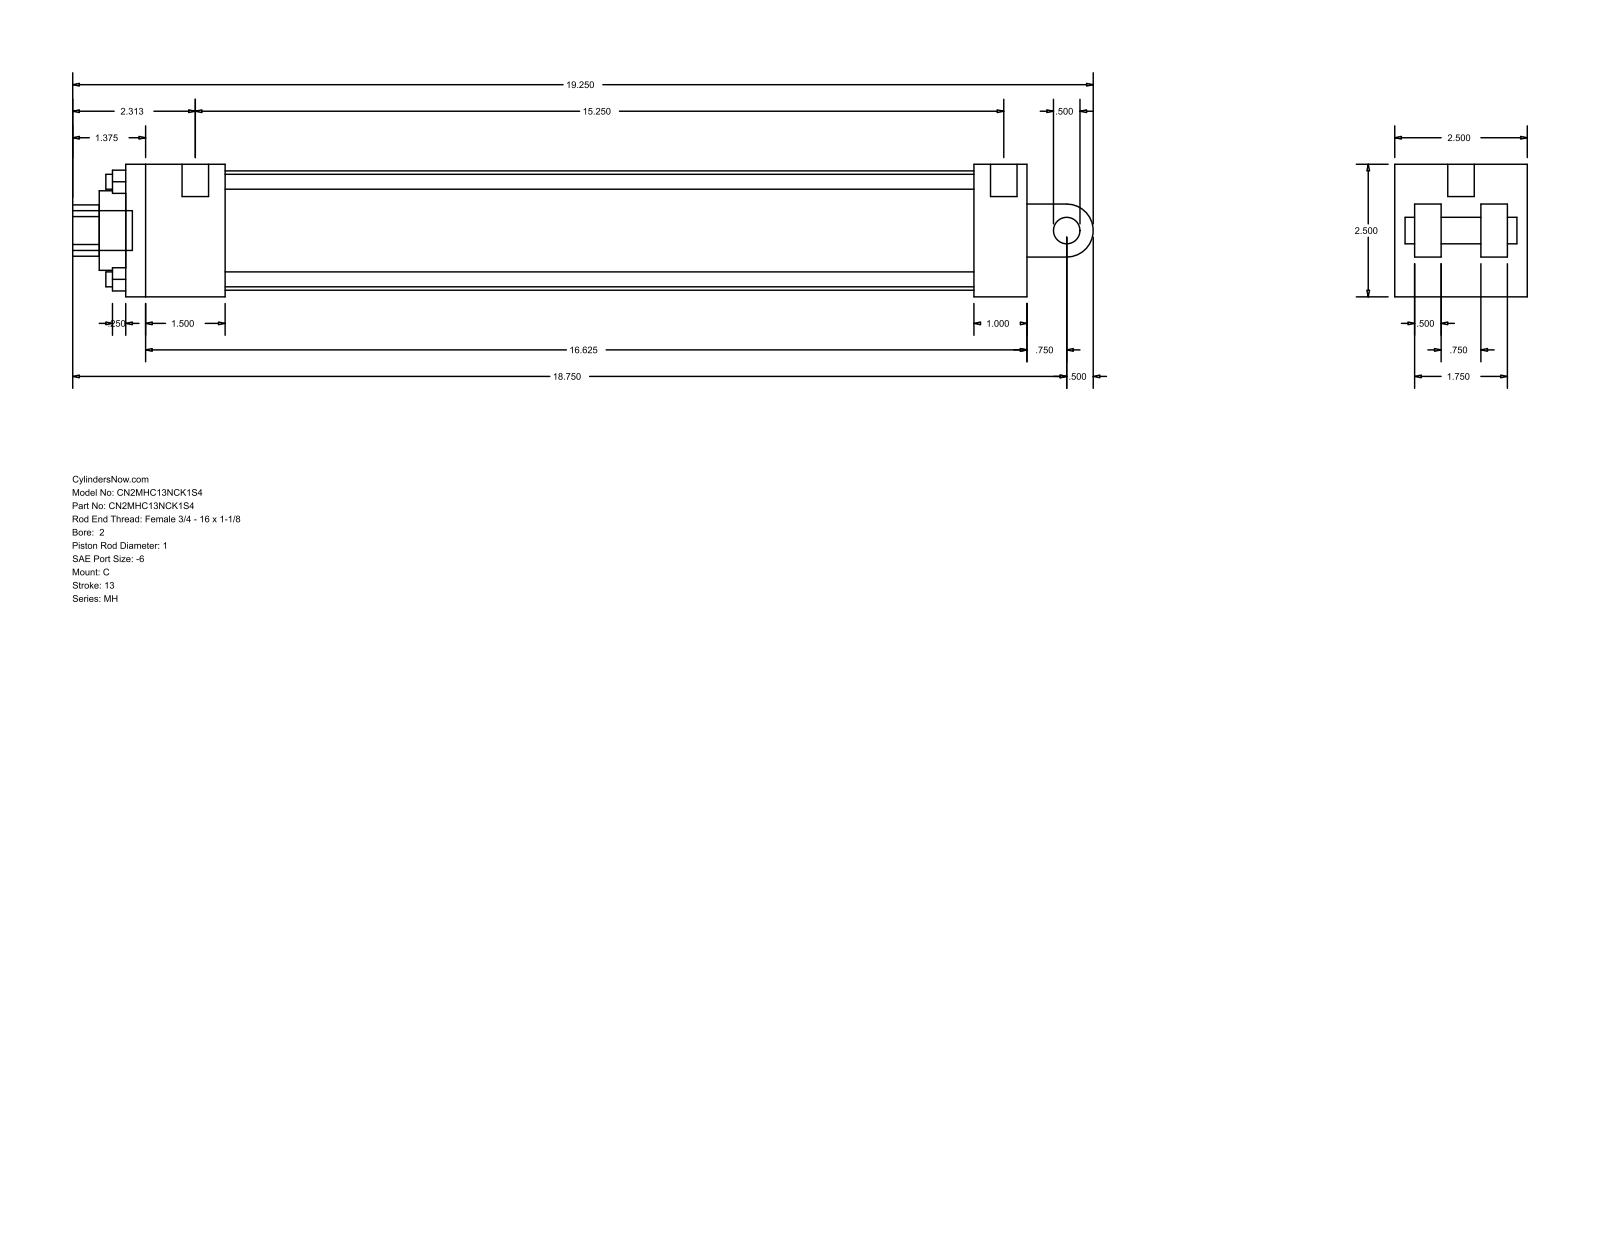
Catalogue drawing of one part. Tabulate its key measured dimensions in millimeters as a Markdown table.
| quantity | value |
| --- | --- |
| part name | MH_C__0200_1 |
| STEP written by | GSSL Pune (CONFIG_CONTROL_DESIGN) |
| units | millimeters |
| bodies | 0 solids, 99 faces (70 planar, 29 cylindrical, 0 other) |
| overall size | 488.95 × 63.5 × 63.5 |
| round holes (diameter × count) | 7.14 × 4, 5.56 × 2, 12.7 × 1, 25.4 × 1, 38.1 × 1, 57.15 × 1 |
| round bosses / shafts (diameter × count) | 12.7 × 2, 5.56 × 2, 19.05 × 1 |
| partial cylindrical surfaces (radius × count) | 12.29 × 1, 12.7 × 1 |
| main face-to-face distances | 63.5, 431.8, 12.7, 25.4, 9.52, 47.63, 53.98, 406.4, 358.77, 384.17 |
| hole center spacings | 33.05, 46.74, 66.1, 3.17 |
